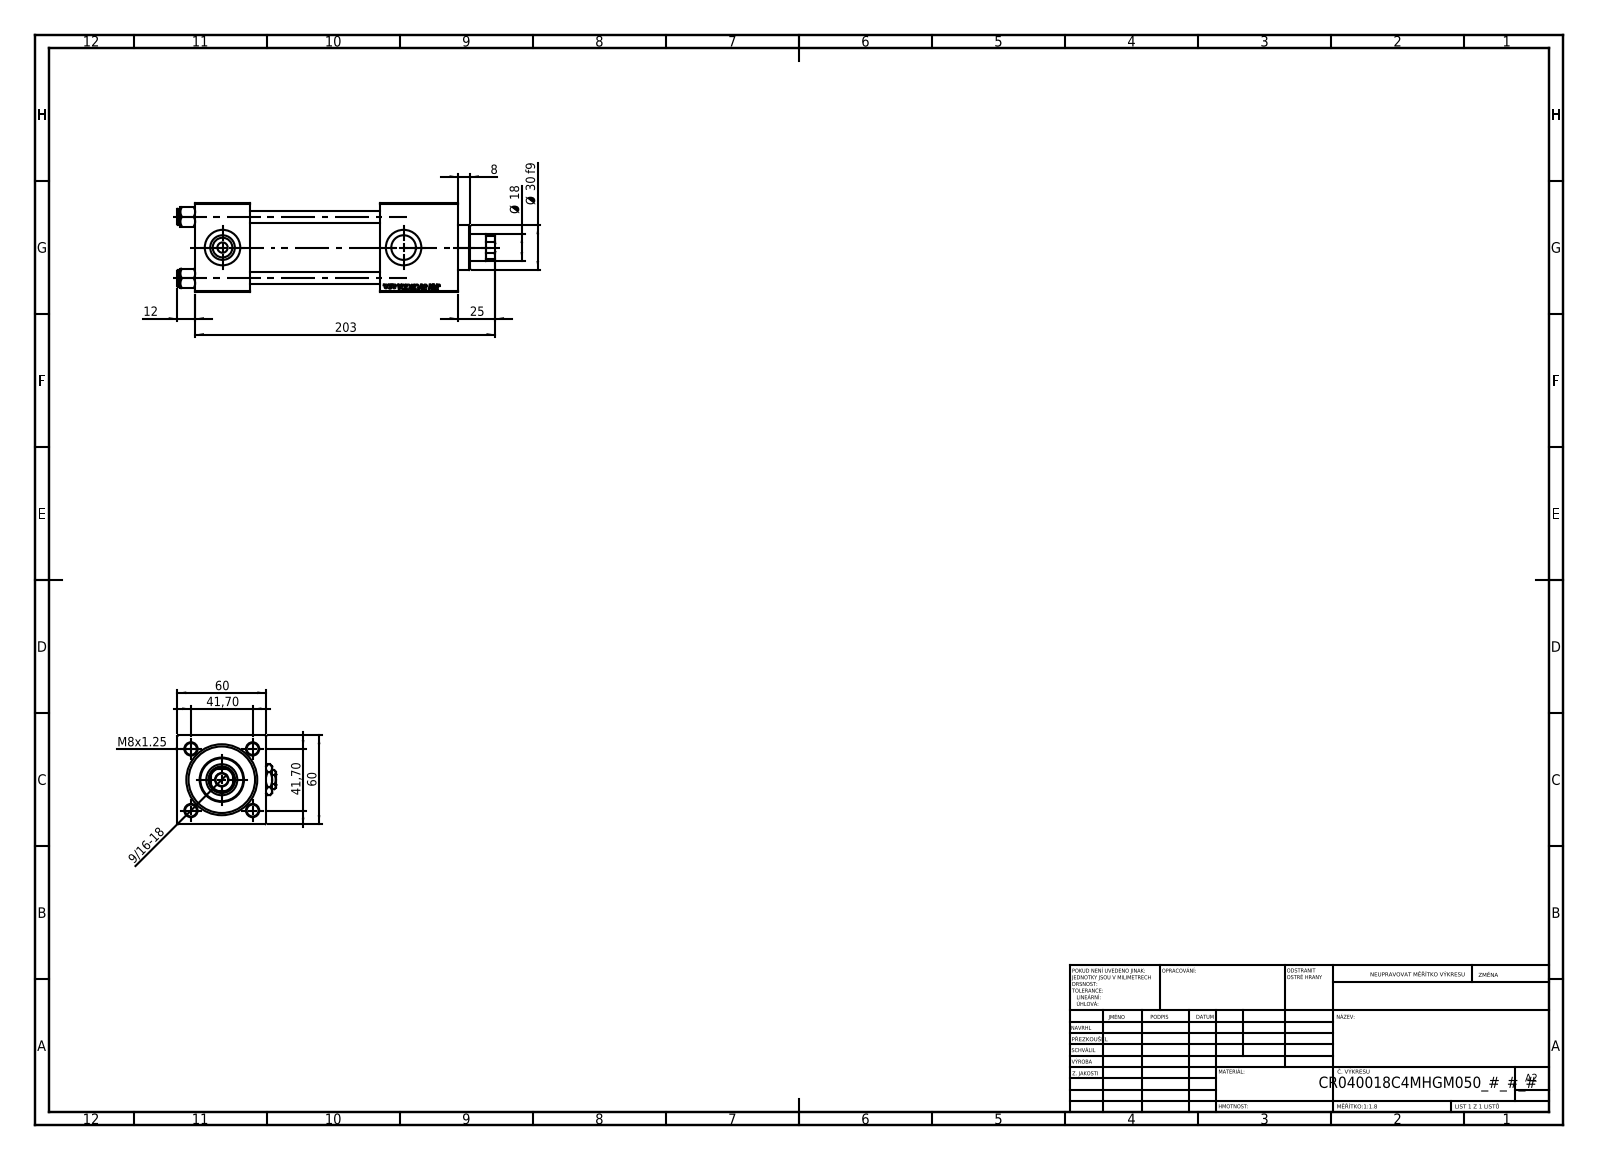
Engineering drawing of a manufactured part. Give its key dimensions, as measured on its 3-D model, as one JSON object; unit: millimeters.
{"part_name": "V215_VC_A; V215CR_C_Body; V215CR_VCP_C; NUT_M5_C (+2 more)", "step_written_by": "SolidWorks 2019 (CONFIG_CONTROL_DESIGN)", "units": "millimeters", "bodies": {"solids": 12, "faces": 1196, "planar": 550, "cylindrical": 90, "other": 556}, "overall_size": [215, 67, 60], "volume_mm3": 426502, "surface_area_mm2": 119414, "round_holes": [[8, 4], [7, 2], [16.66, 2], [24, 2], [8.5, 1], [18, 1], [21, 1], [31, 1], [40, 1], [45, 1]], "round_bosses_or_shafts": [[11, 4], [46, 1], [30, 1]], "partial_cylinders_radius": [[8.5, 1]], "face_to_face_distances": [60, 37, 178, 141, 53, 125, 88, 149.3, 112.3, 24.3], "hole_center_spacings": [29.49, 41.7, 58.97, 122.5]}
